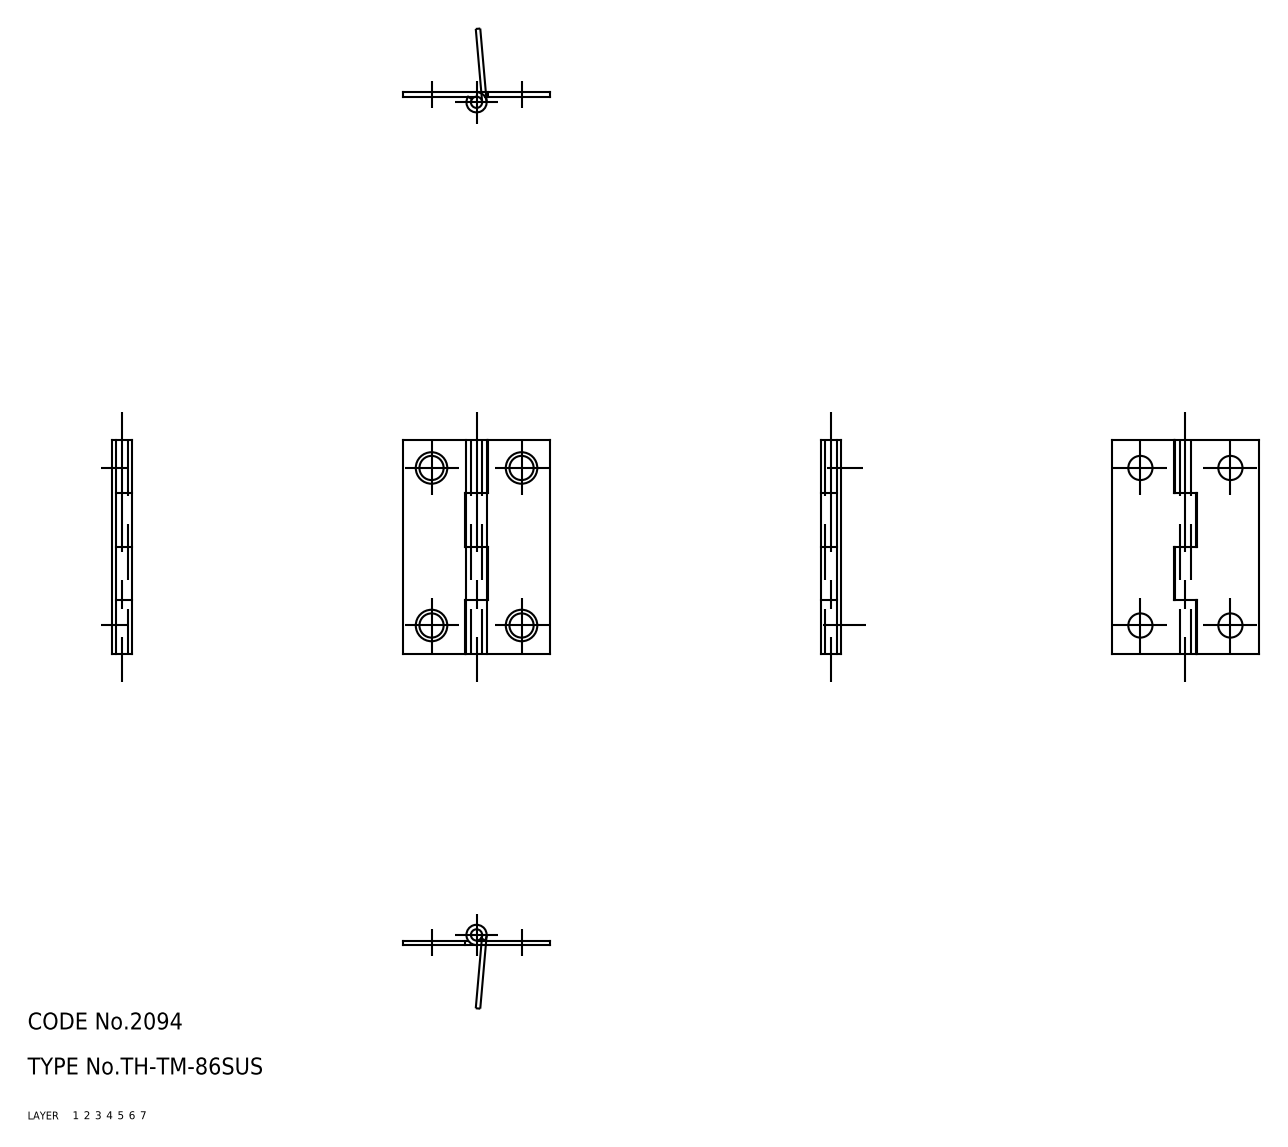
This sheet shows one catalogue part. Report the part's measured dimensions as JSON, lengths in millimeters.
{"part_name": "shaft; hinge piece_B; hinge piece_A; TH_TM_86SUS_26294_36", "step_written_by": "CADfix (AUTOMOTIVE_DESIGN)", "units": "millimeters", "bodies": {"solids": 3, "faces": 52, "planar": 0, "cylindrical": 0, "other": 52}, "overall_size": [38, 26, 3.6], "volume_mm3": 1014, "surface_area_mm2": 2755}
